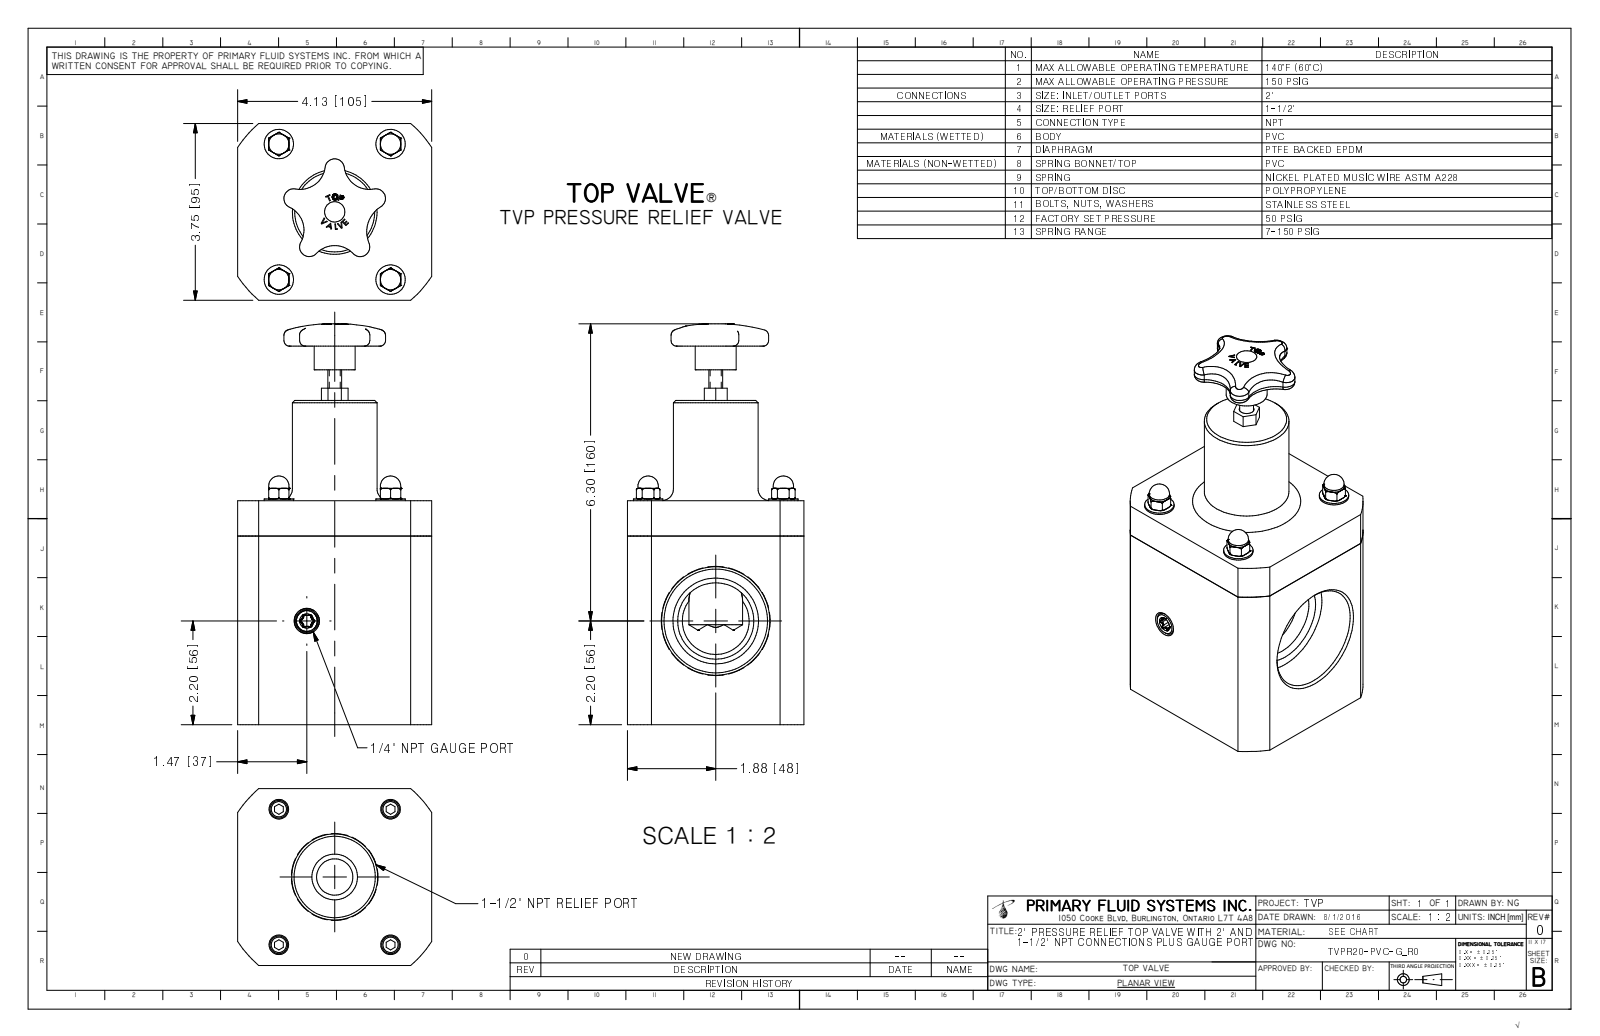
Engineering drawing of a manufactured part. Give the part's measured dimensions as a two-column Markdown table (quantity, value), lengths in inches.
| quantity | value |
| --- | --- |
| part name | TVPR20-PVC-G_R0 |
| STEP written by | Autodesk Inventor 2009 (AUTOMOTIVE_DESIGN) |
| units | inches |
| bodies | 1 solid, 362 faces (153 planar, 52 cylindrical, 157 other) |
| overall size | 8.5 × 4.125 × 3.75 |
| volume | 69.34 in³ |
| surface area | 145.5 in² |
| round holes (diameter × count) | 0.175 × 4, 1.727 × 1, 2.2 × 1 |
| round bosses / shafts (diameter × count) | 0.625 × 4, 0.433 × 4, 0.375 × 4, 1.8 × 1, 0.87 × 1, 0.293 × 1 |
| partial cylindrical surfaces (radius × count) | 0.027 × 6, 0.085 × 5, 0.205 × 5, 0.536 × 4, 0.656 × 4, 0.625 × 1, 0.745 × 1, 2.475 × 1 |
| main face-to-face distances | 3.75, 0.9, 4.75, 4.125, 3.225, 2.325, 3.85, 6.875, 5.975, 2.125 |
| hole center spacings | 1.864, 1.865, 2.375, 2.875, 3.729 |
